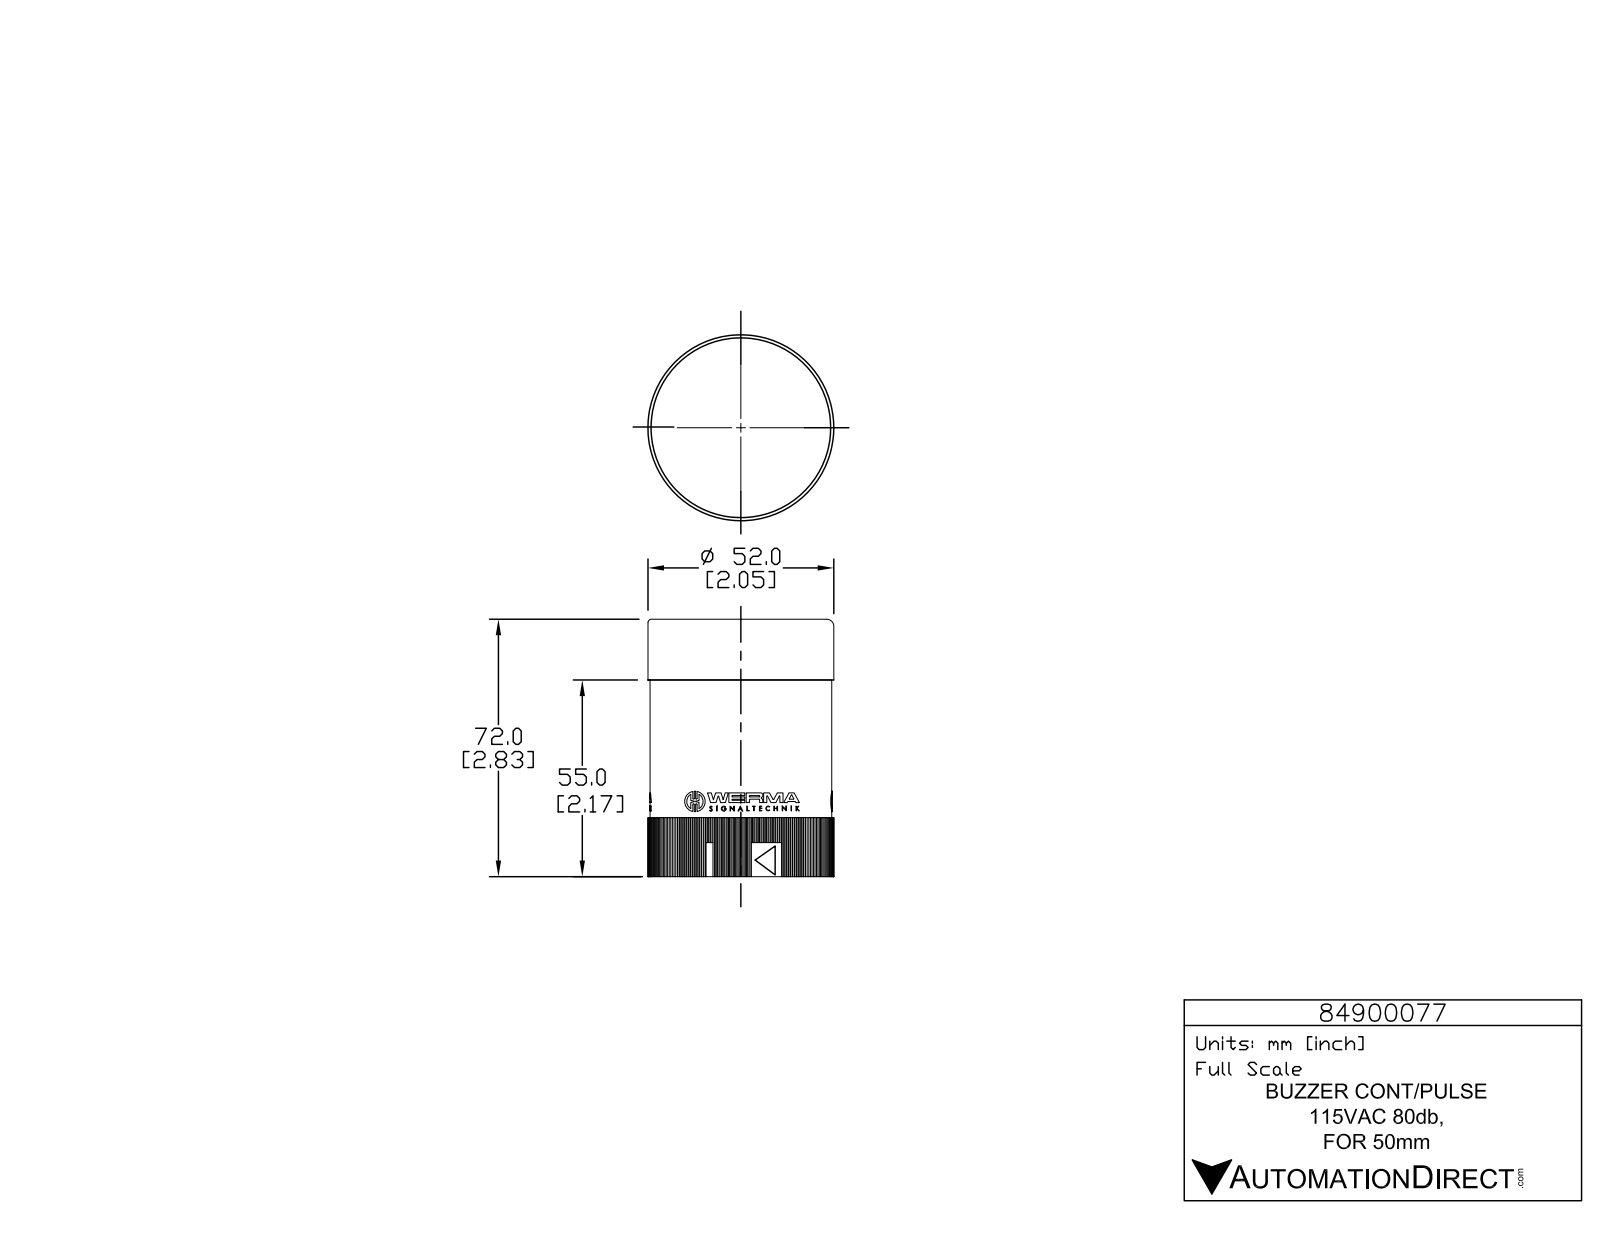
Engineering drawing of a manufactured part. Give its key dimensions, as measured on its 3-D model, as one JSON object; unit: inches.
{"part_name": "84900077", "step_written_by": "SolidWorks 2015 (AUTOMOTIVE_DESIGN)", "units": "inches", "bodies": {"solids": 1, "faces": 1267, "planar": 1020, "cylindrical": 245, "other": 2}, "overall_size": [2.835, 2.047, 2.047], "volume_in3": 7.75, "surface_area_in2": 29.28, "round_holes": [[0.039, 3], [1.898, 1]], "round_bosses_or_shafts": [[0.226, 3], [0.056, 3], [2.047, 1], [2.002, 1]], "partial_cylinders_radius": [[0.008, 6], [0.008, 6], [0.008, 6], [0.131, 6], [0.004, 3], [0.005, 3], [0.008, 3], [0.008, 3]], "face_to_face_distances": [2.363, 1.428, 1.429, 1.429, 2.835, 0.472, 1.428, 1.428, 0.67, 1.693]}
